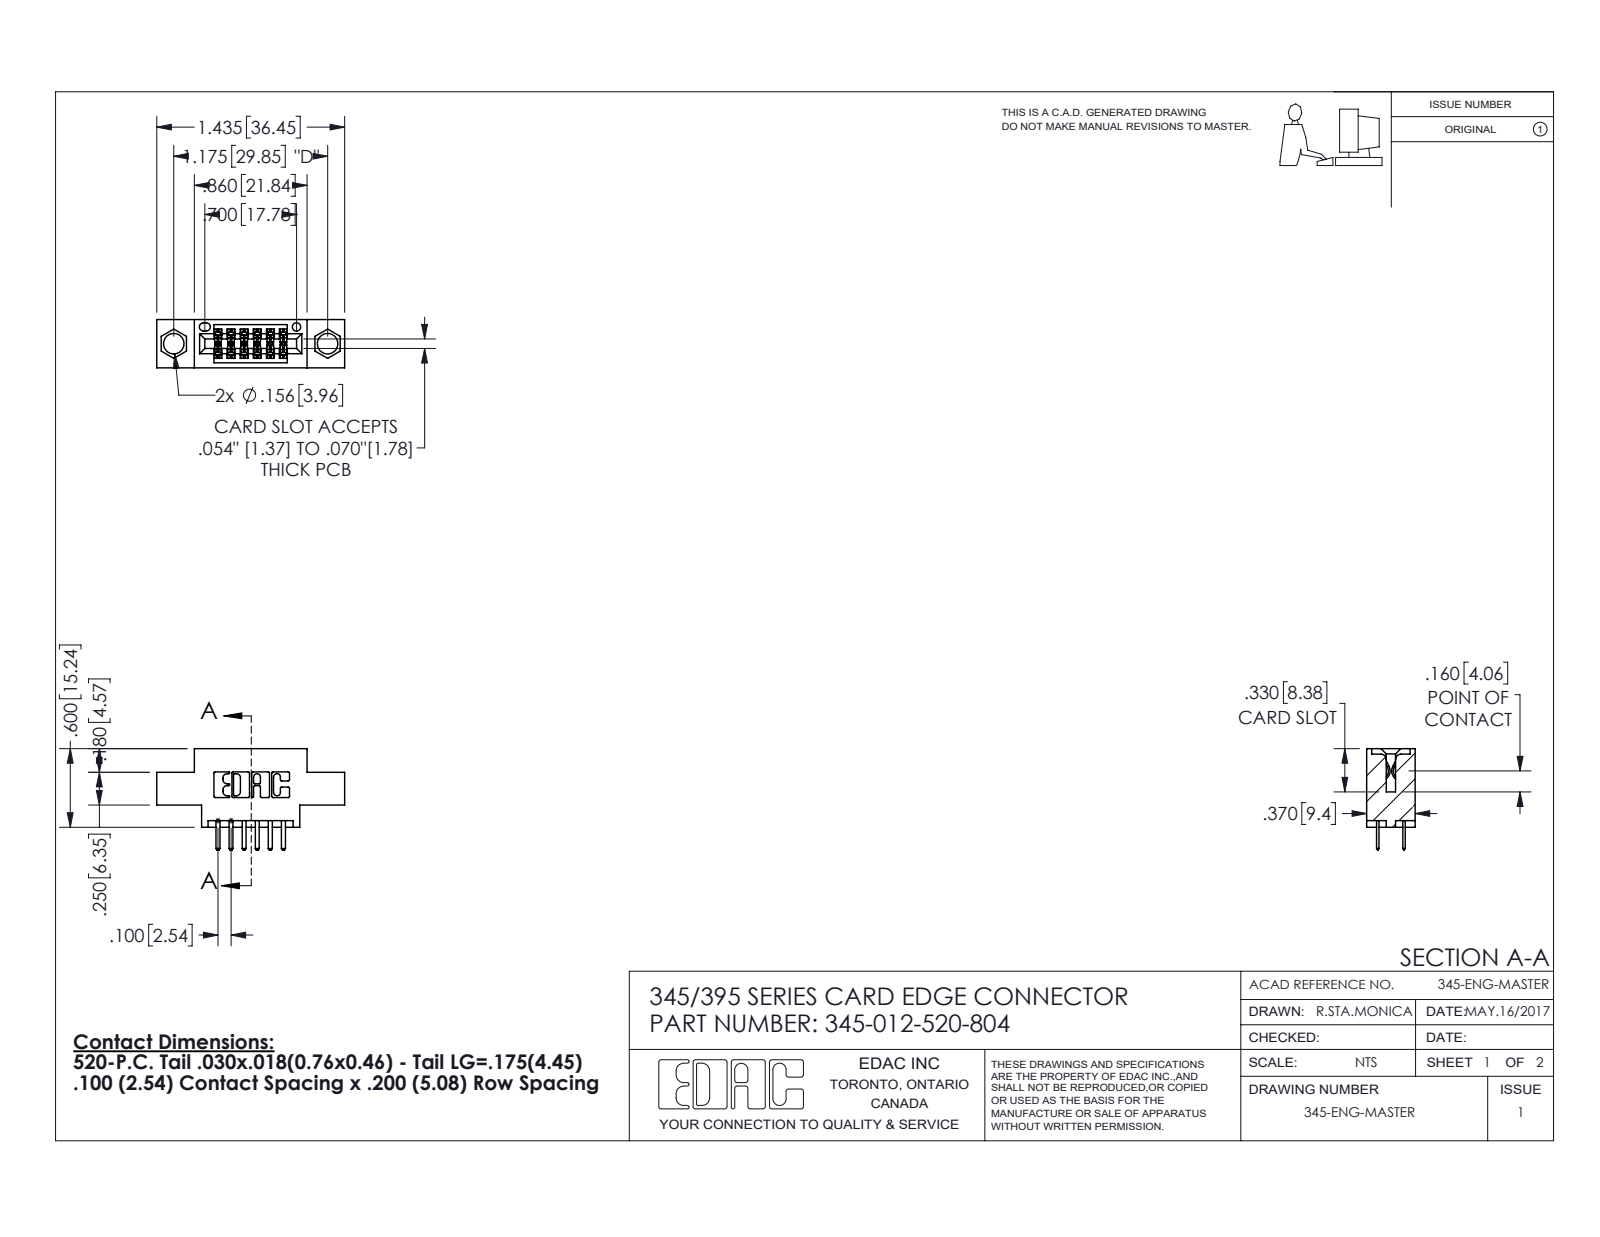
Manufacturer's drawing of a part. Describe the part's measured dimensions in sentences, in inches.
The part is named "345-012-520-804; 345 Part_0.170 Offset - 0.156 Dia-TI; 345-292-001_345-293-120". Its 3-D file was written by "SolidWorks 2020 (CONFIG_CONTROL_DESIGN)". It is 13 solids with 792 faces: 518 planar, 274 cylindrical and 0 other. Overall it measures 1.435 by 0.775 by 0.37 inches. Its volume is 0.182 cubic inches and its surface area 5.726 square inches. Round holes: 2 of diameter 0.156, 1 of diameter 0.064. Partial cylindrical surfaces (rounded edges, fillets, slot ends): 22 of radius 0.01, 19 of radius 0.006, 16 of radius 0.01, 6 of radius 0.007, 6 of radius 0.031, 3 of radius 0.026, 2 of radius 0.014, 2 of radius 0.019. The main face-to-face distances are 0.2, 0.37, 0.1, 0.072, 0.298, 0.025, 0.098, 0.272, 0.06, 0.3. The hole center spacings are 0.27, 0.946, 1.175.
